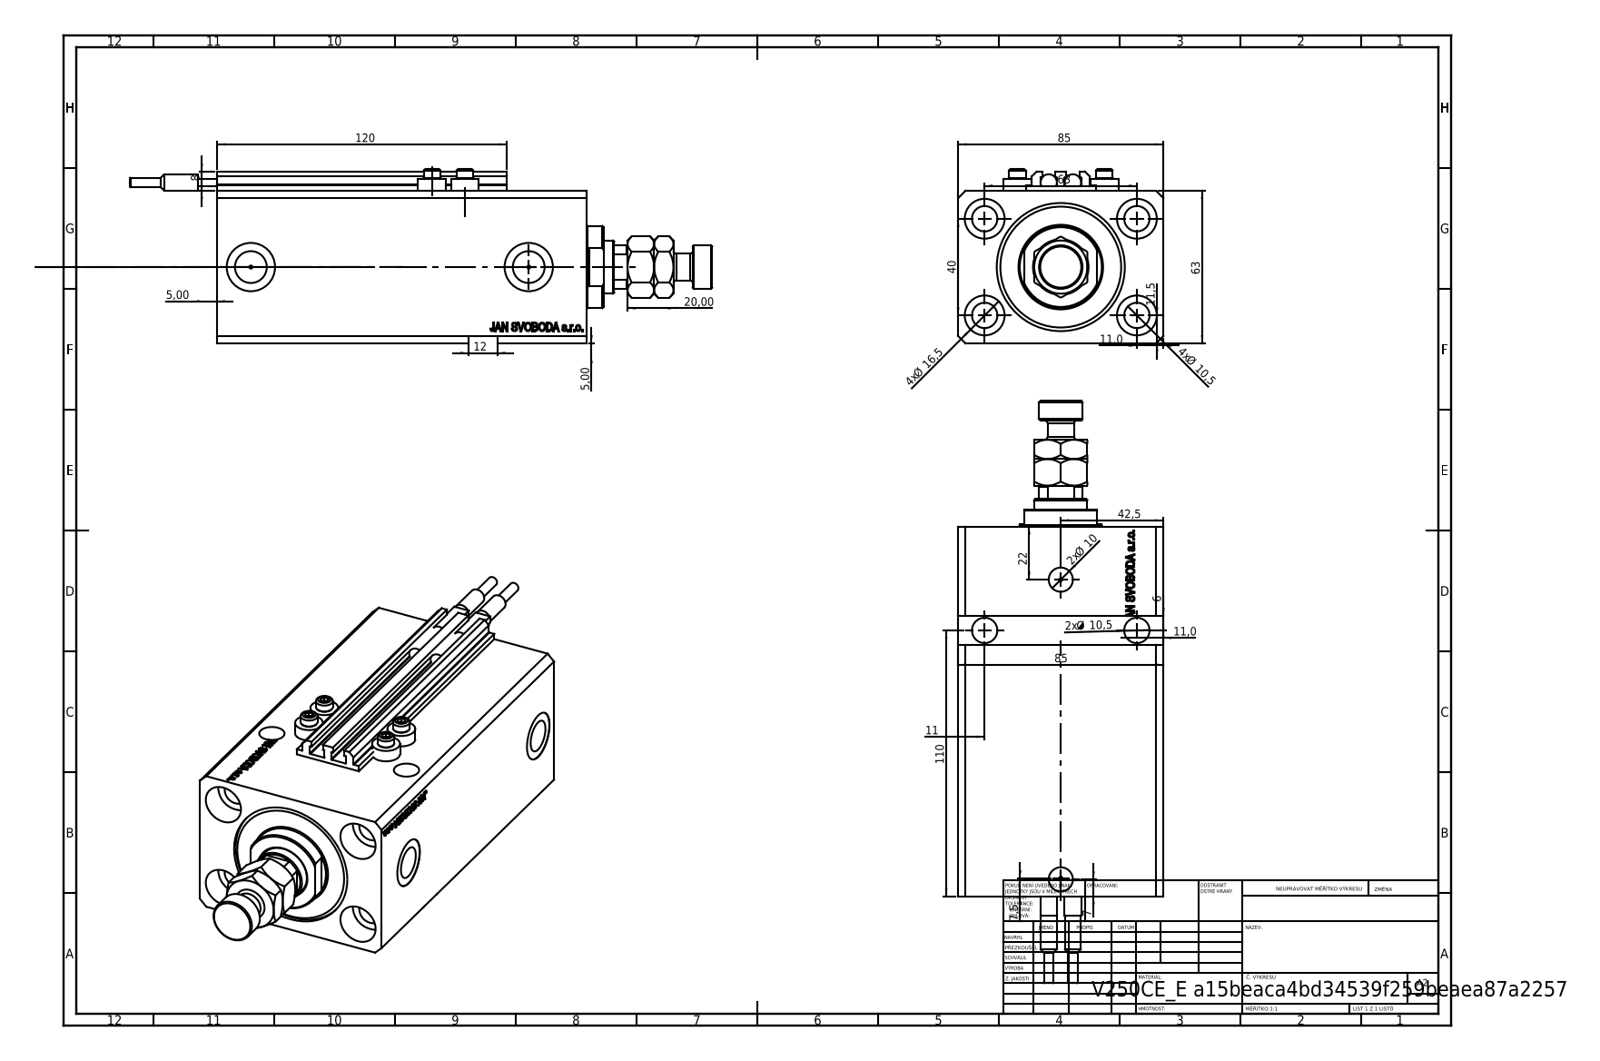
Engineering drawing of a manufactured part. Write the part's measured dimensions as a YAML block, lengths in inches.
part_name: "MFA; ALLEN BOLT V250CE; V250CE_VC_E; V250CE_E_Body (+2 more)"
step_written_by: "SolidWorks 2019 (CONFIG_CONTROL_DESIGN)"
units: inches
bodies: {solids: 11, faces: 1207, planar: 587, cylindrical: 154, other: 466}
overall_size: [9.484, 3.346, 2.835]
volume: 42.86
surface_area: 229.5
round_holes:
  - {diameter: 0.413, count: 6}
  - {diameter: 0.049, count: 4}
  - {diameter: 0.157, count: 4}
  - {diameter: 0.65, count: 4}
  - {diameter: 0.394, count: 2}
  - {diameter: 0.518, count: 2}
  - {diameter: 0.787, count: 2}
  - {diameter: 0.492, count: 1}
  - {diameter: 0.866, count: 1}
  - {diameter: 1.575, count: 1}
  - {diameter: 2.087, count: 1}
round_bosses_or_shafts:
  - {diameter: 0.457, count: 4}
  - {diameter: 0.276, count: 4}
  - {diameter: 0.268, count: 2}
  - {diameter: 0.256, count: 2}
  - {diameter: 0.157, count: 2}
  - {diameter: 1.339, count: 1}
  - {diameter: 0.709, count: 1}
  - {diameter: 0.433, count: 1}
partial_cylinders:
  - {radius: 0.008, count: 10}
  - {radius: 0.413, count: 1}
face_to_face_distances: [2.48, 3.346, 6.024, 4.957, 1.067, 2.559, 0.449, 4.508, 5.575, 0.118]
hole_center_spacings: [1.469, 2.48, 0.535, 0.606, 0.983, 1.324, 1.417, 1.491]
